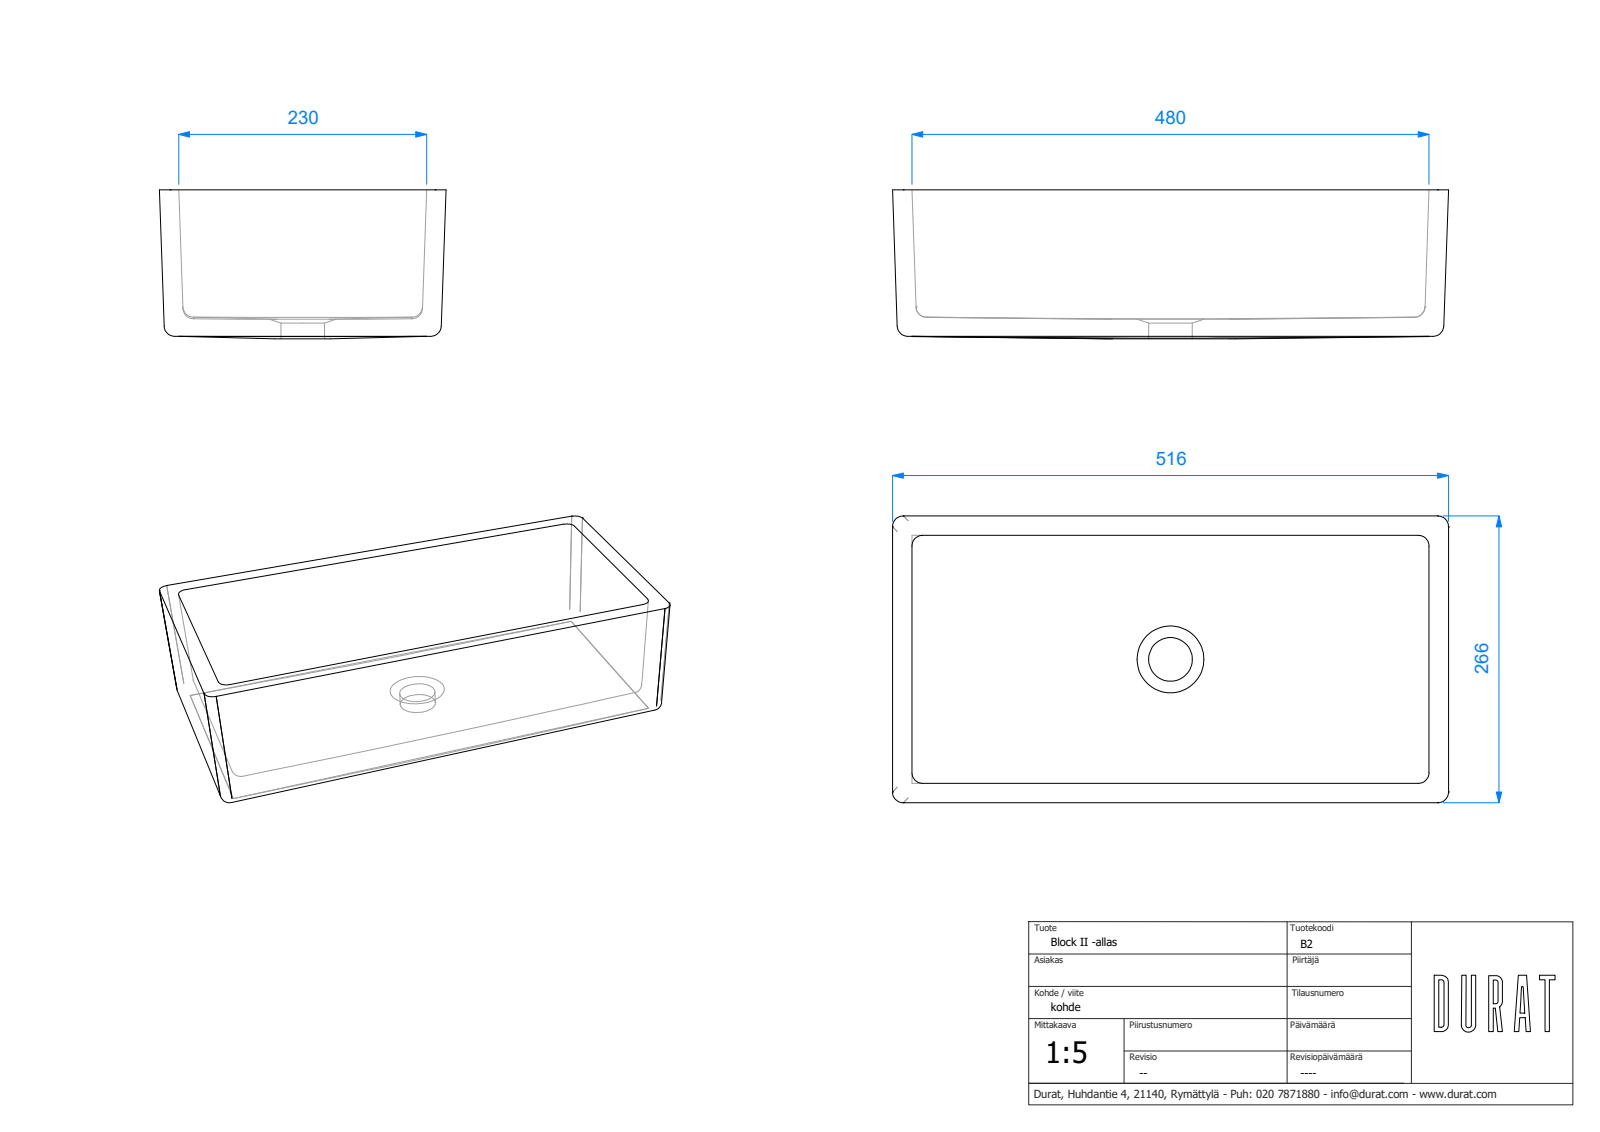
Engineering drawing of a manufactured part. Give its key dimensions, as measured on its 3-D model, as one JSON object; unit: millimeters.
{"step_written_by": "ST-DEVELOPER v15 (AUTOMOTIVE_DESIGN)", "units": "millimeters", "bodies": {"solids": 0, "faces": 48, "planar": 16, "cylindrical": 0, "other": 32}, "overall_size": [516.02, 266.02, 138.19], "face_to_face_distances": [18.01, 17.98, 17.97, 138.19, 18, 120.19, 2.19, 15.81, 136, 230]}
